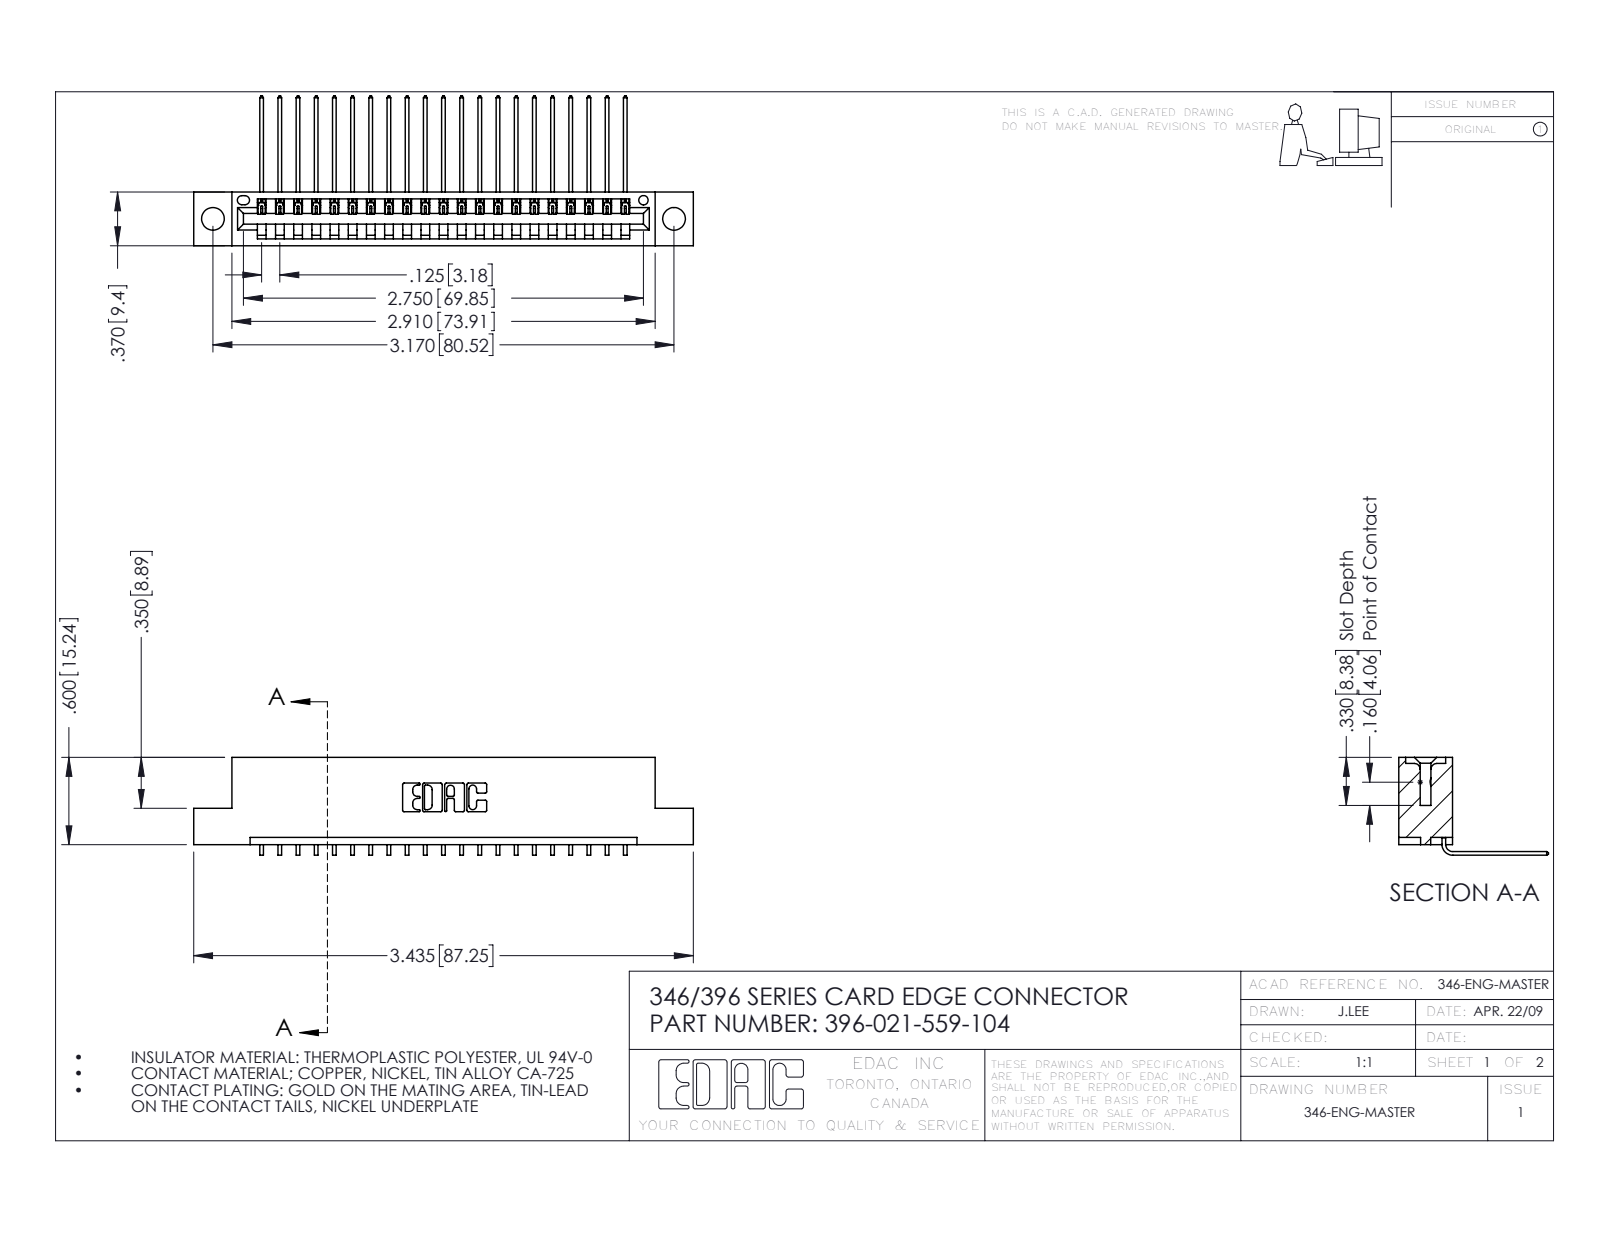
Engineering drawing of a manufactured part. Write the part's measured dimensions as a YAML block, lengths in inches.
part_name: "396-021-559-104; 345-292-001_558 559 Tail - 1; 346 Part_Flush Mounting Lugs - 0.156 Dia-TH"
step_written_by: "SolidWorks 2016 (CONFIG_CONTROL_DESIGN)"
units: inches
bodies: {solids: 22, faces: 1382, planar: 958, cylindrical: 424, other: 0}
overall_size: [3.435, 1.03, 0.673]
volume: 0.5
surface_area: 15.86
round_holes:
  - {diameter: 0.156, count: 2}
  - {diameter: 0.064, count: 1}
partial_cylinders:
  - {radius: 0.006, count: 42}
  - {radius: 0.01, count: 22}
  - {radius: 0.007, count: 6}
  - {radius: 0.031, count: 6}
  - {radius: 0.026, count: 3}
  - {radius: 0.031, count: 2}
  - {radius: 0.04, count: 2}
  - {radius: 0.014, count: 1}
face_to_face_distances: [0.048, 0.322, 0.37, 0.25, 0.072, 0.025, 0.298, 0.148, 0.222, 0.1]
hole_center_spacings: [0.246, 2.963, 3.17]
